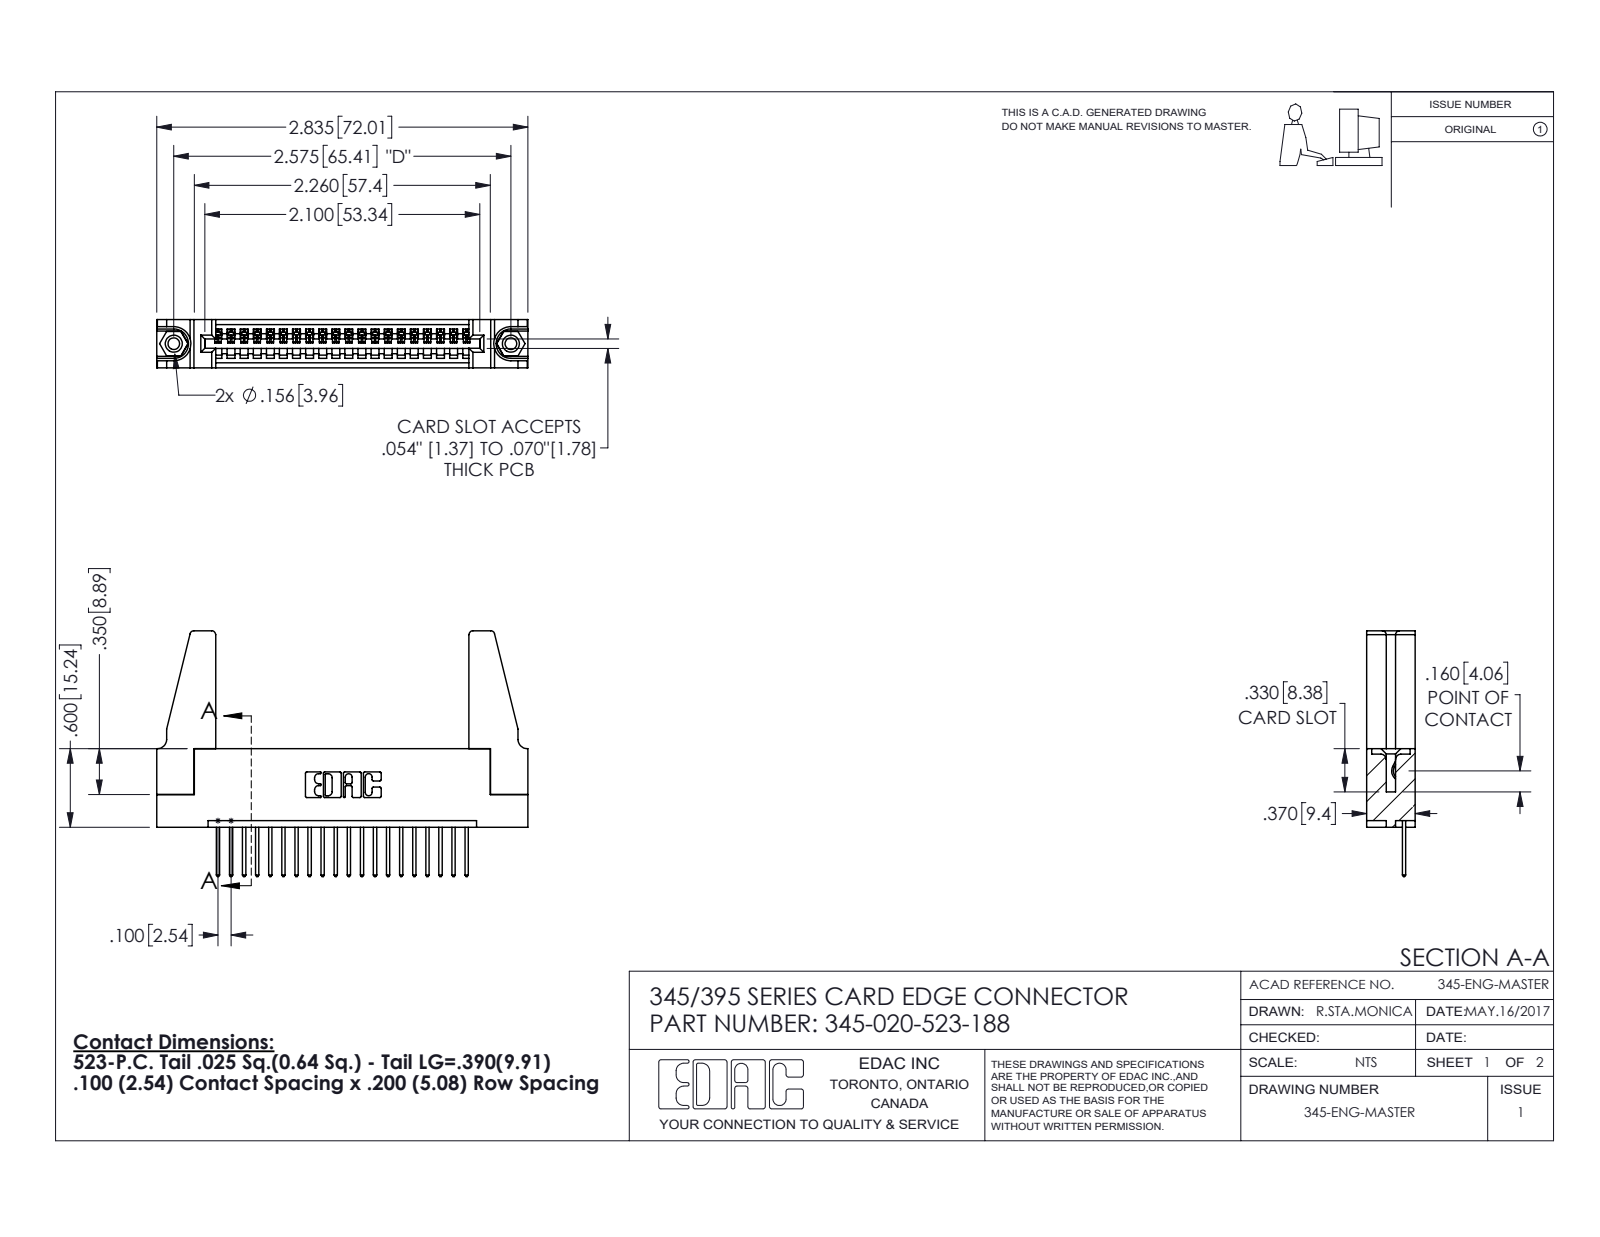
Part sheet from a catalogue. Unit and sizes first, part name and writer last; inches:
Units: inches
Overall size (bounding box): 2.836 × 1.877 × 0.37
Round holes (diameter × count): ⌀0.089 ×2, ⌀0.125 ×2, ⌀0.156 ×2, ⌀0.064 ×1
Round bosses / shafts (diameter × count): ⌀0.155 ×2
Partial cylindrical surfaces — rounded edges, fillets, slot ends (radius × count): R0.006 ×40, R0.01 ×40, R0.01 ×22, R0.03 ×8, R0.007 ×6, R0.031 ×6, R0.026 ×3, R0.031 ×2
Main face-to-face distances: 0.37, 0.072, 0.298, 0.2, 0.098, 0.272, 0.025, 0.225, 0.149, 0.148
Hole centre spacings: 0.27, 2.341, 2.575
Volume: 0.605 in³ · Surface area: 18.13 in²
Bodies: 25 solids, 1410 faces (952 planar, 442 cylindrical, 16 other)
Part name (STEP PRODUCT): 345-220-078_345-220-088; 345-020-523-188; 345-292-001_345-293-123; 345 Part_Flush Mounting Lugs - 0.156 Dia-TH (+1 more)
STEP written by: SolidWorks 2016 (CONFIG_CONTROL_DESIGN)
